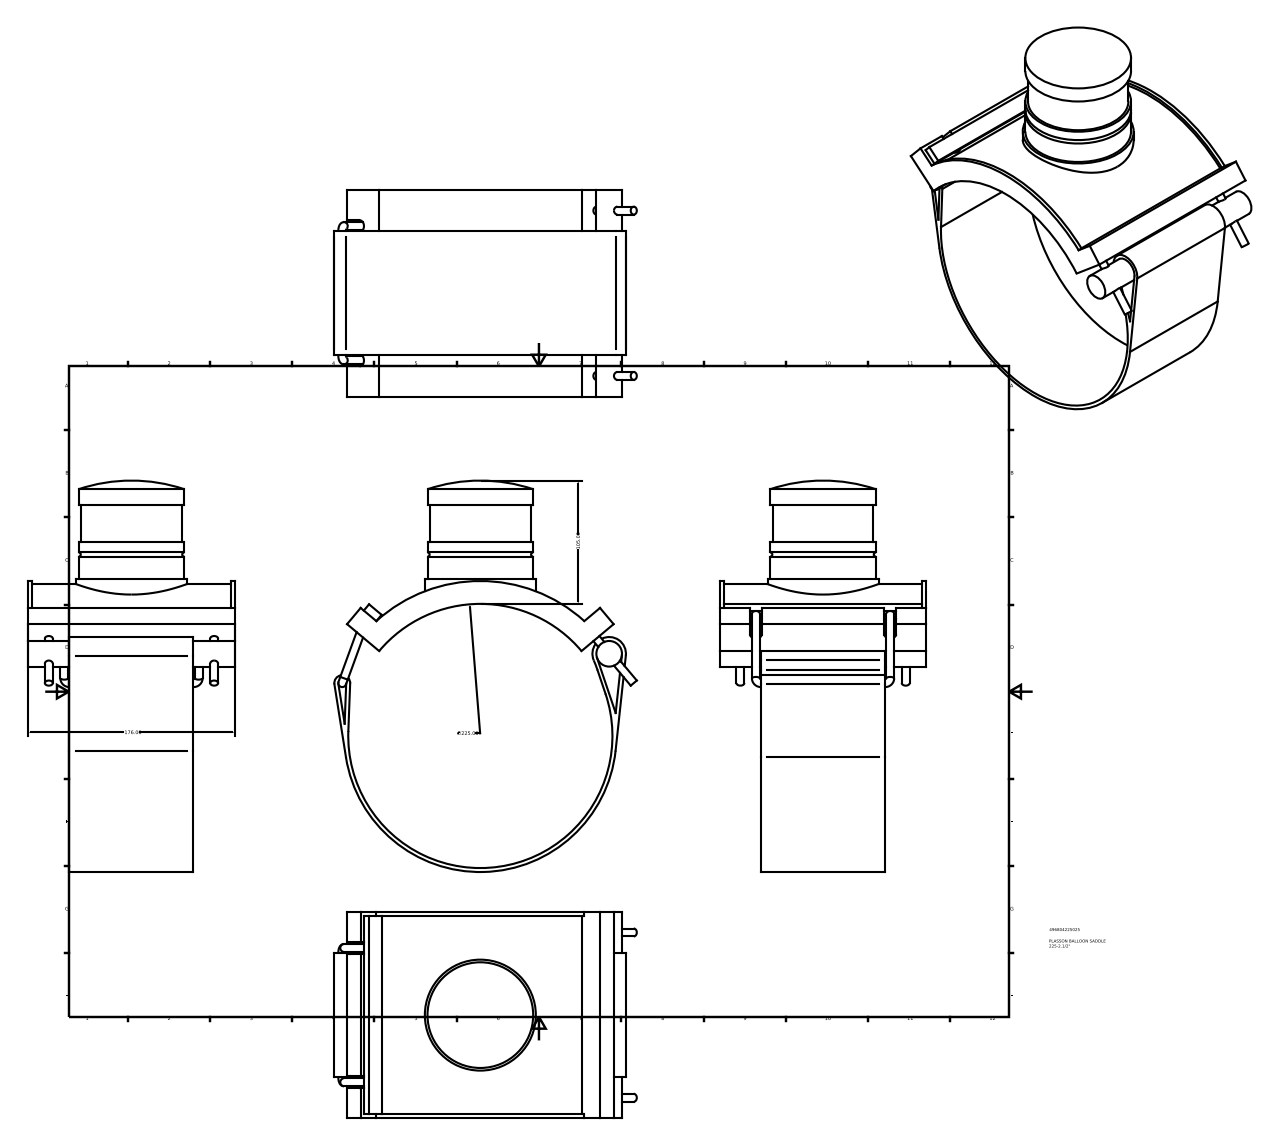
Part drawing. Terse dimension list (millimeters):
name: 496804225025
written by: Autodesk Inventor 2015 (AUTOMOTIVE_DESIGN)
unit: mm
bodies: 2 solids, 72 faces (43 planar, 25 cylindrical, 4 other)
size: 333.38 × 257.63 × 176
volume: 1 600 000 mm³; area: 290 781 mm²
holes: 1× ⌀225
bosses: 4× ⌀6.75, 1× ⌀94.5, 1× ⌀90, 1× ⌀85.5, 1× ⌀21.81
rounds: 2× R5.06, 1× R3.38, 1× R6.75, 1× R14.28, 1× R112.5, 1× R115.88, 1× R129.38, 1× R131.96
face distances: 3.37, 176, 35.2, 140.8, 17.98, 24.98, 2.96, 105.6, 18.01, 6.97
